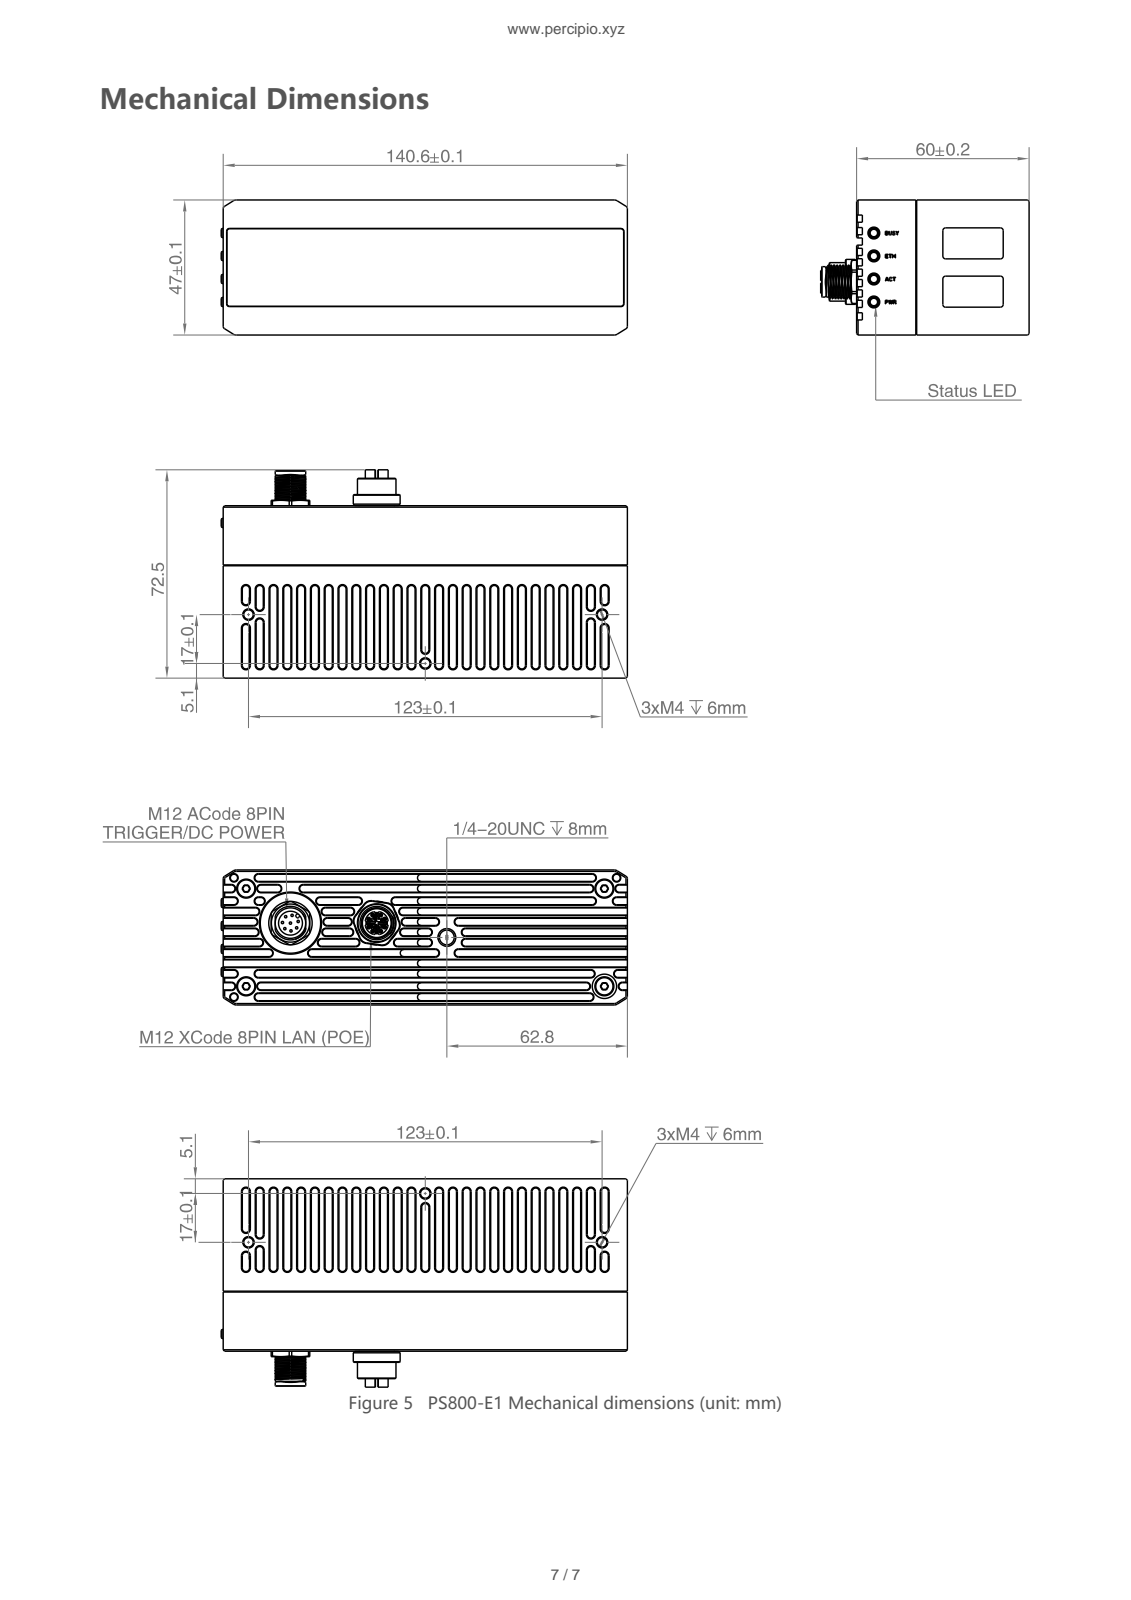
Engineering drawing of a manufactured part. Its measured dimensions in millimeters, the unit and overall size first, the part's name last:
Units: millimetres
Overall size (bounding box): 309.74 × 234.55 × 175.91
Round holes (diameter × count): ⌀0.65 ×8, ⌀0.7 ×8, ⌀1.17 ×8, ⌀1.24 ×8, ⌀2.68 ×4, ⌀3.5 ×4, ⌀2.5 ×3, ⌀3.3 ×3, ⌀6.6 ×3, ⌀5.11 ×1, ⌀8.3 ×1, ⌀8.5 ×1
Round bosses / shafts (diameter × count): ⌀1.1 ×8, ⌀0.8 ×8, ⌀6 ×4, ⌀2.5 ×4, ⌀15.4 ×2, ⌀18 ×1, ⌀13.4 ×1, ⌀11.9 ×1
Partial cylindrical surfaces — rounded edges, fillets, slot ends (radius × count): R1.25 ×126, R1 ×24, R0.1 ×20, R0.4 ×11, R0.3 ×10, R0.96 ×8, R0.5 ×7, R3 ×6
Main face-to-face distances: 2, 2.5, 47, 1.2, 45, 37.75, 43, 7.96, 26.04, 11.71
Hole centre spacings: 3.13, 4.43, 1.98, 2.8, 5.6, 5.94, 6.26, 5.67
Volume: 361 839 mm³ · Surface area: 325 646 mm²
Bodies: 2 solids, 2518 faces (1295 planar, 603 cylindrical, 620 other)
Part name (STEP PRODUCT): PS800-E1-STR
STEP written by: CREO PARAMETRIC BY PTC INC, 2022164 (CONFIG_CONTROL_DESIGN)
